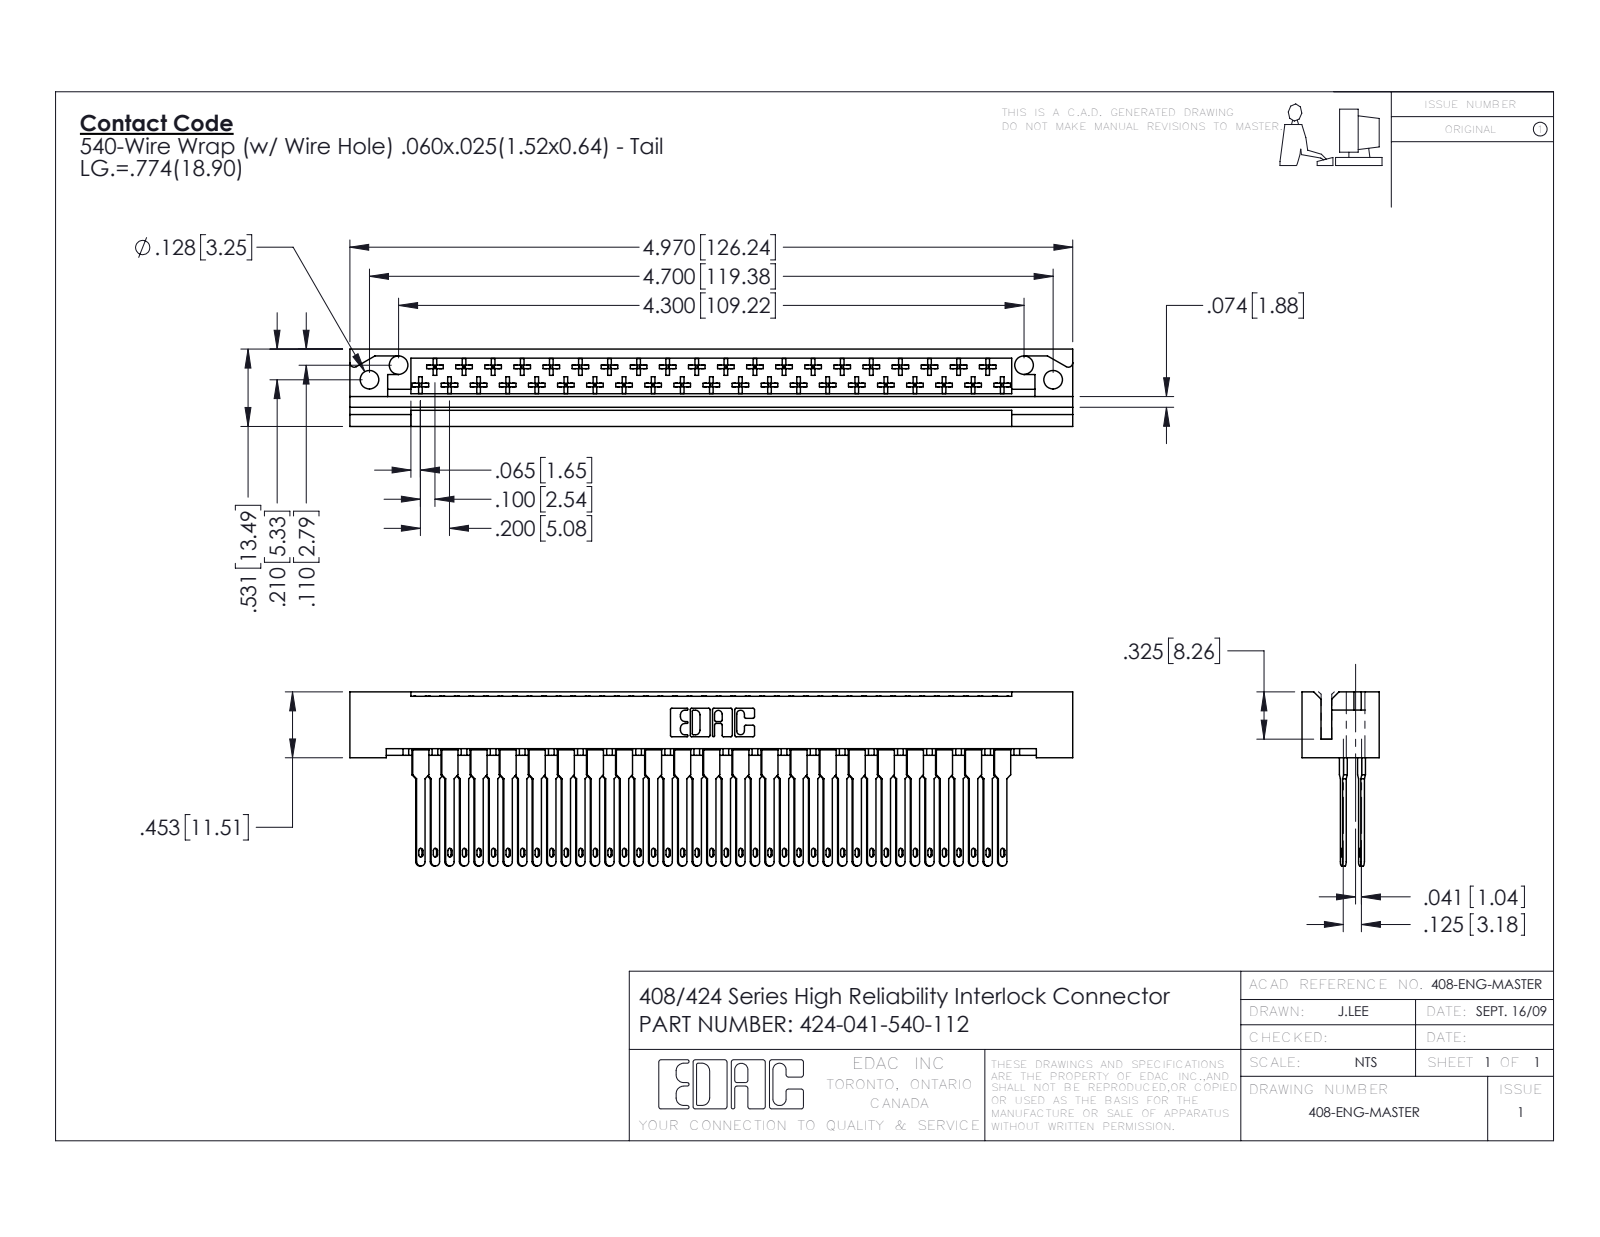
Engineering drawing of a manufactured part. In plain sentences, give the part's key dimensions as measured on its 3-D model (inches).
The part is named "424 Part_041; 424-041-540-112; 408-290-001_408-290-140". Its 3-D file was written by "SolidWorks 2016 (CONFIG_CONTROL_DESIGN)". It is 42 solids with 2482 faces: 1811 planar, 507 cylindrical and 164 other. Overall it measures 4.97 by 1.197 by 0.531 inches. Its volume is 0.889 cubic inches and its surface area 31.45 square inches. Round holes: 4 of diameter 0.128. Partial cylindrical surfaces (rounded edges, fillets, slot ends): 246 of radius 0.01, 82 of radius 0.015, 43 of radius 0.02, 43 of radius 0.03, 22 of radius 0.01, 6 of radius 0.007, 6 of radius 0.031, 3 of radius 0.026. The main face-to-face distances are 0.025, 0.531, 0.125, 0.4, 0.1, 0.235, 0.259, 0.272, 0.025, 0.296. The hole center spacings are 0.224, 4.501, 4.3, 4.7.
